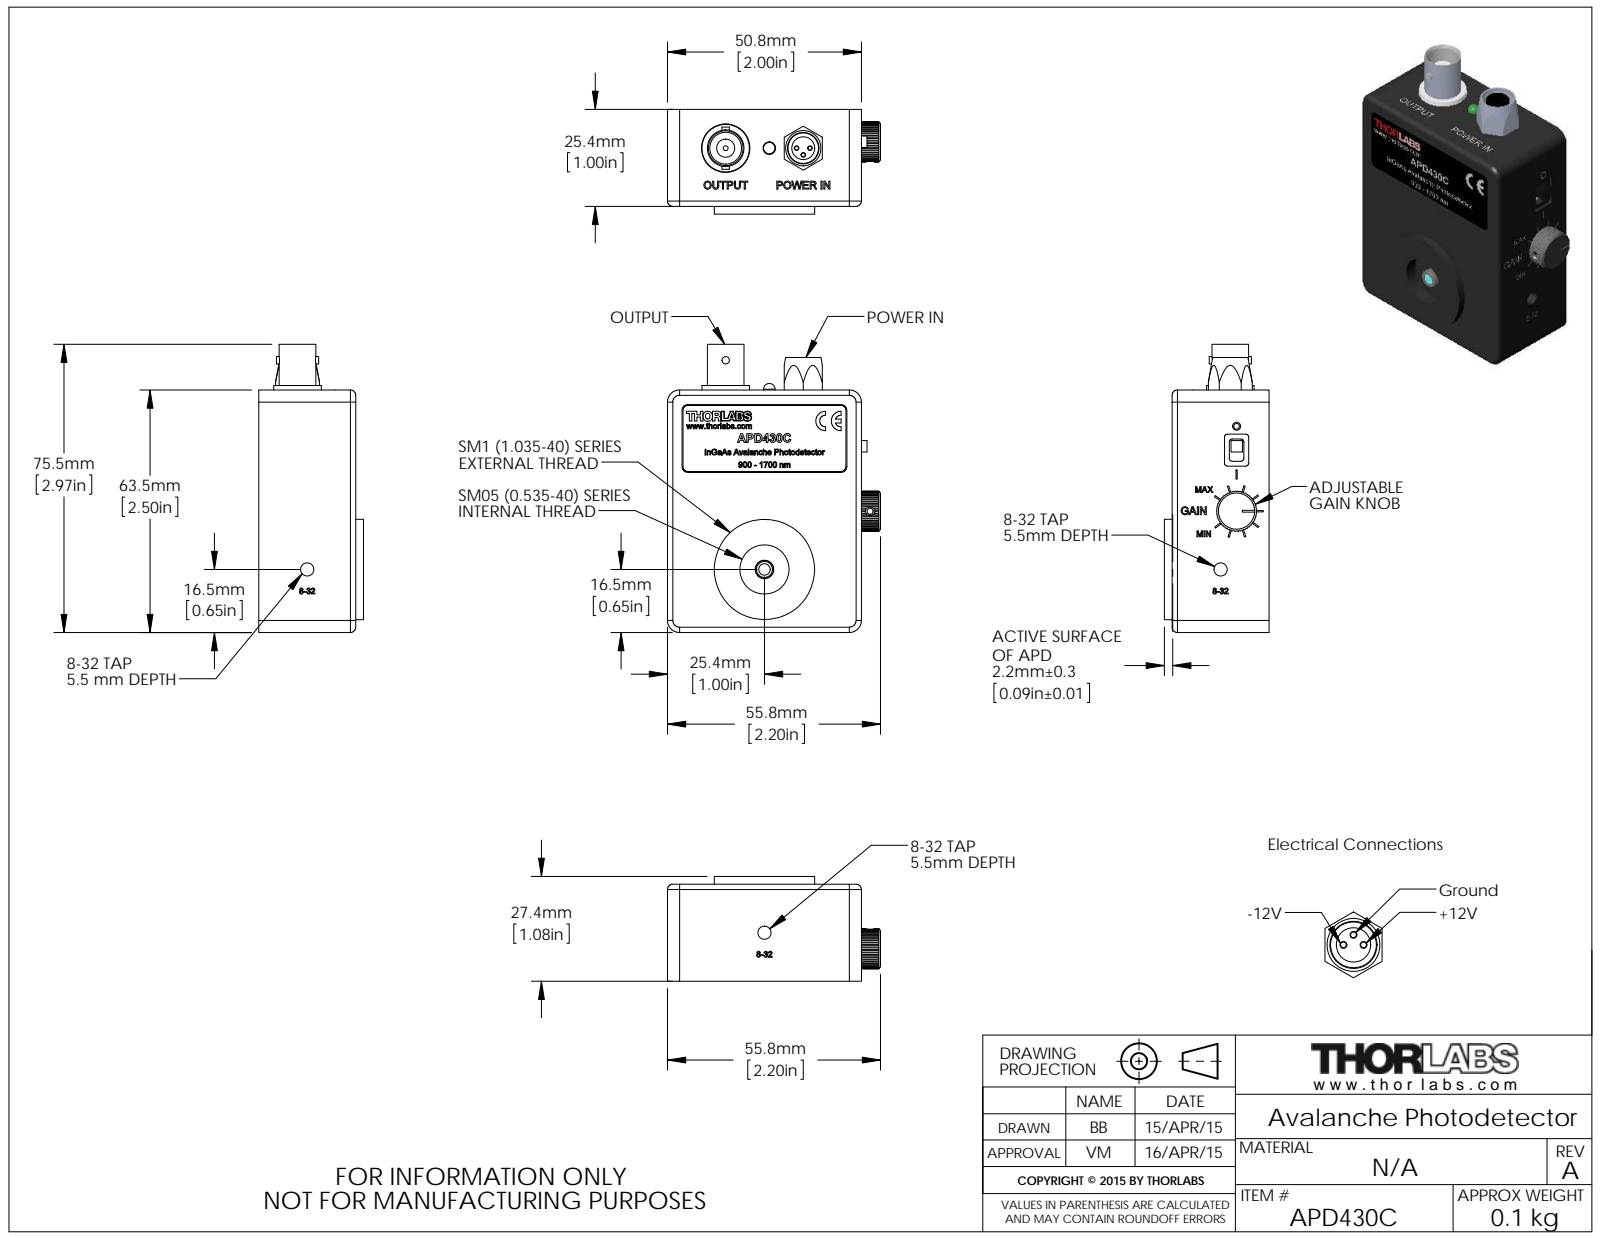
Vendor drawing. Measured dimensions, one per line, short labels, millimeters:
name: RK09K1110-15; flat head screw_am_B18.6.7M - M2 x 0.4 x 4 Type I Cross Recessed FHMS --4N; M0092-0545-0A-Deckel; RKMF-01-3polig_RKMF4 (+8 more)
written by: SolidWorks 2014 (AUTOMOTIVE_DESIGN)
unit: mm
bodies: 4 solids, 2515 faces (1261 planar, 472 cylindrical, 782 other)
size: 75.46 × 55.8 × 27.43
volume: 32 195 mm³; area: 34 500 mm²
holes: 9× ⌀1.6, 6× ⌀0.51, 6× ⌀0.81, 4× ⌀2.4, 4× ⌀2.44, 3× ⌀0.46, 2× ⌀0.45, 2× ⌀2.5, 2× ⌀3.45, 1× ⌀1.27, 1× ⌀1.32, 1× ⌀2.1
bosses: 5× ⌀1, 4× ⌀3.8, 4× ⌀2, 2× ⌀1.64, 2× ⌀1.6, 2× ⌀1.3, 1× ⌀26.29, 1× ⌀12.45
rounds: 53× R0.3, 19× R3.17, 14× R3.3, 10× R0.8, 8× R0.79, 8× R2.41, 6× R0.5, 6× R1.91
face distances: 1.59, 13.08, 11.49, 2.54, 11.48, 9.89, 1.6, 0.4, 23.81, 10.67
hole spacings: 41.17, 2.54, 20.89, 39.38, 4.41, 16.46, 21.35, 51.14
